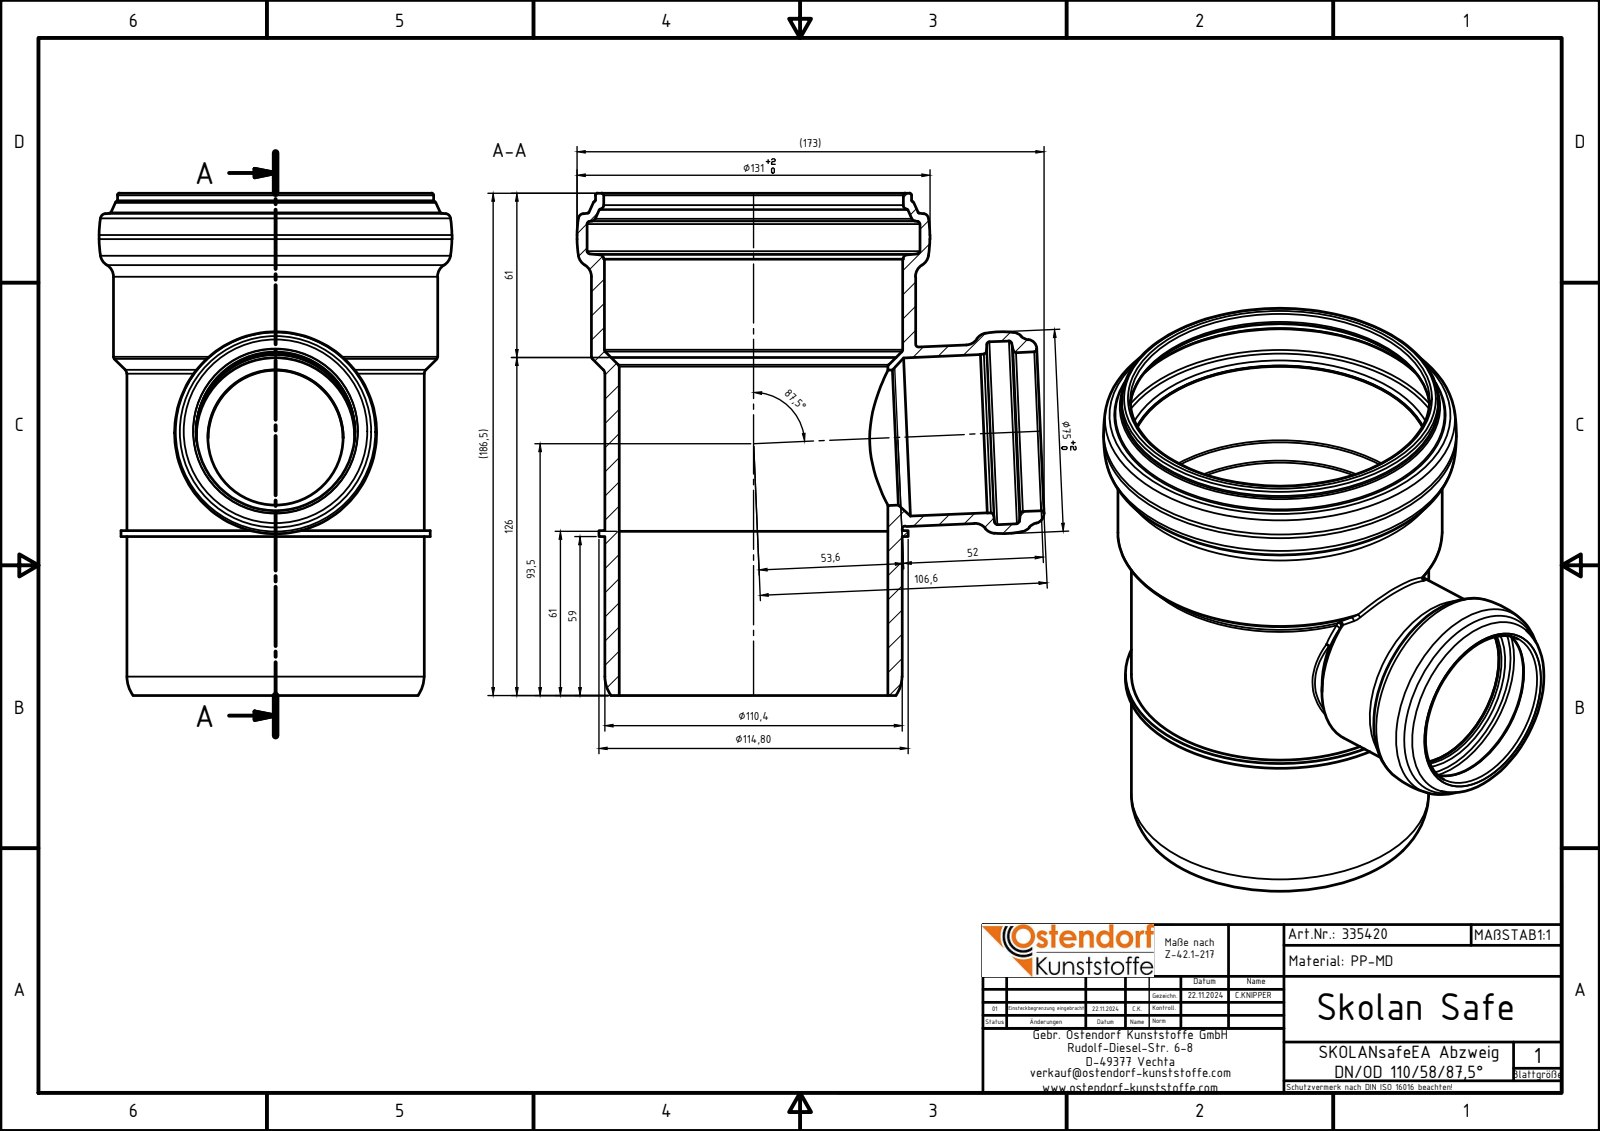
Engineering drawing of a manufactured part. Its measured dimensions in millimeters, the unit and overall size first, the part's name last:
Units: millimetres
Overall size (bounding box): 186.5 × 173.34 × 131
Round holes (diameter × count): ⌀59 ×2, ⌀50.2 ×1, ⌀58.8 ×1, ⌀67.9 ×1, ⌀99.8 ×1, ⌀110.8 ×1, ⌀111.2 ×1, ⌀123.6 ×1
Round bosses / shafts (diameter × count): ⌀131 ×1, ⌀120.4 ×1, ⌀117.4 ×1, ⌀114.8 ×1, ⌀110.4 ×1, ⌀66.4 ×1
Partial cylindrical surfaces — rounded edges, fillets, slot ends (radius × count): R29.1 ×1
Main face-to-face distances: 59, 61.2, 2.2, 186.5, 127.5, 125.3, 162, 103, 100.8, 24.5
Volume: 368 552 mm³ · Surface area: 158 929 mm²
Bodies: 1 solid, 86 faces (7 planar, 19 cylindrical, 60 other)
Part name (STEP PRODUCT): 335420z
STEP written by: Autodesk Inventor 2024 (AUTOMOTIVE_DESIGN)
